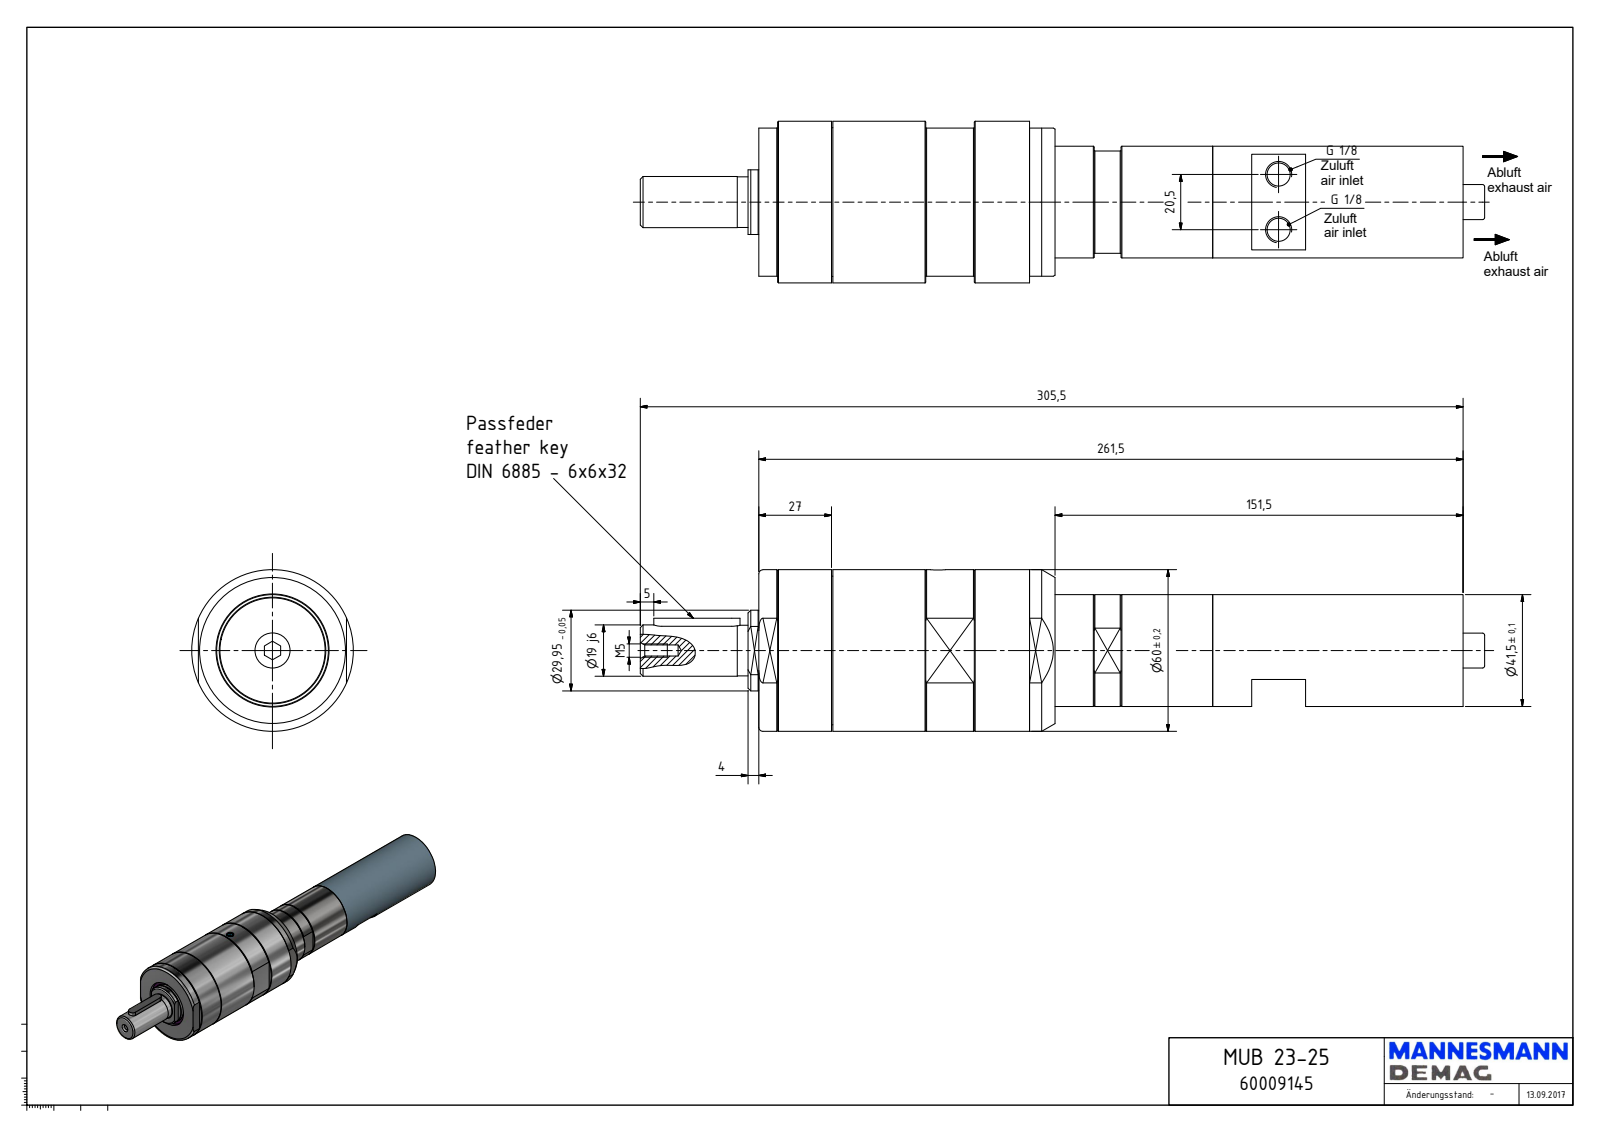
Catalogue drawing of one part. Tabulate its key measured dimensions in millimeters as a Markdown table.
| quantity | value |
| --- | --- |
| part name | MUB 23-25_60009145 |
| STEP written by | Autodesk Inventor 2018 (AUTOMOTIVE_DESIGN) |
| units | millimeters |
| bodies | 1 solid, 177 faces (77 planar, 62 cylindrical, 38 other) |
| overall size | 313.5 × 60 × 60 |
| volume | 518 430 mm³ |
| surface area | 56 960 mm² |
| round holes (diameter × count) | 8.57 × 2, 1.55 × 1, 4 × 1, 4.13 × 1, 5.5 × 1, 8.5 × 1, 35 × 1, 39.5 × 1, 42 × 1, 55.38 × 1 |
| round bosses / shafts (diameter × count) | 60 × 1, 55.18 × 1, 41.5 × 1, 39 × 1, 36 × 1, 29.95 × 1, 19 × 1, 18.8 × 1 |
| partial cylindrical surfaces (radius × count) | 1 × 2, 1.6 × 2, 2 × 2, 2.5 × 2, 3 × 2, 8 × 1, 8.1 × 1, 12.92 × 1 |
| main face-to-face distances | 261.5, 110, 151.5, 55, 78.5, 82.5, 27.5, 234, 31, 104.5 |
| hole center spacings | 126.91, 20.5 |
